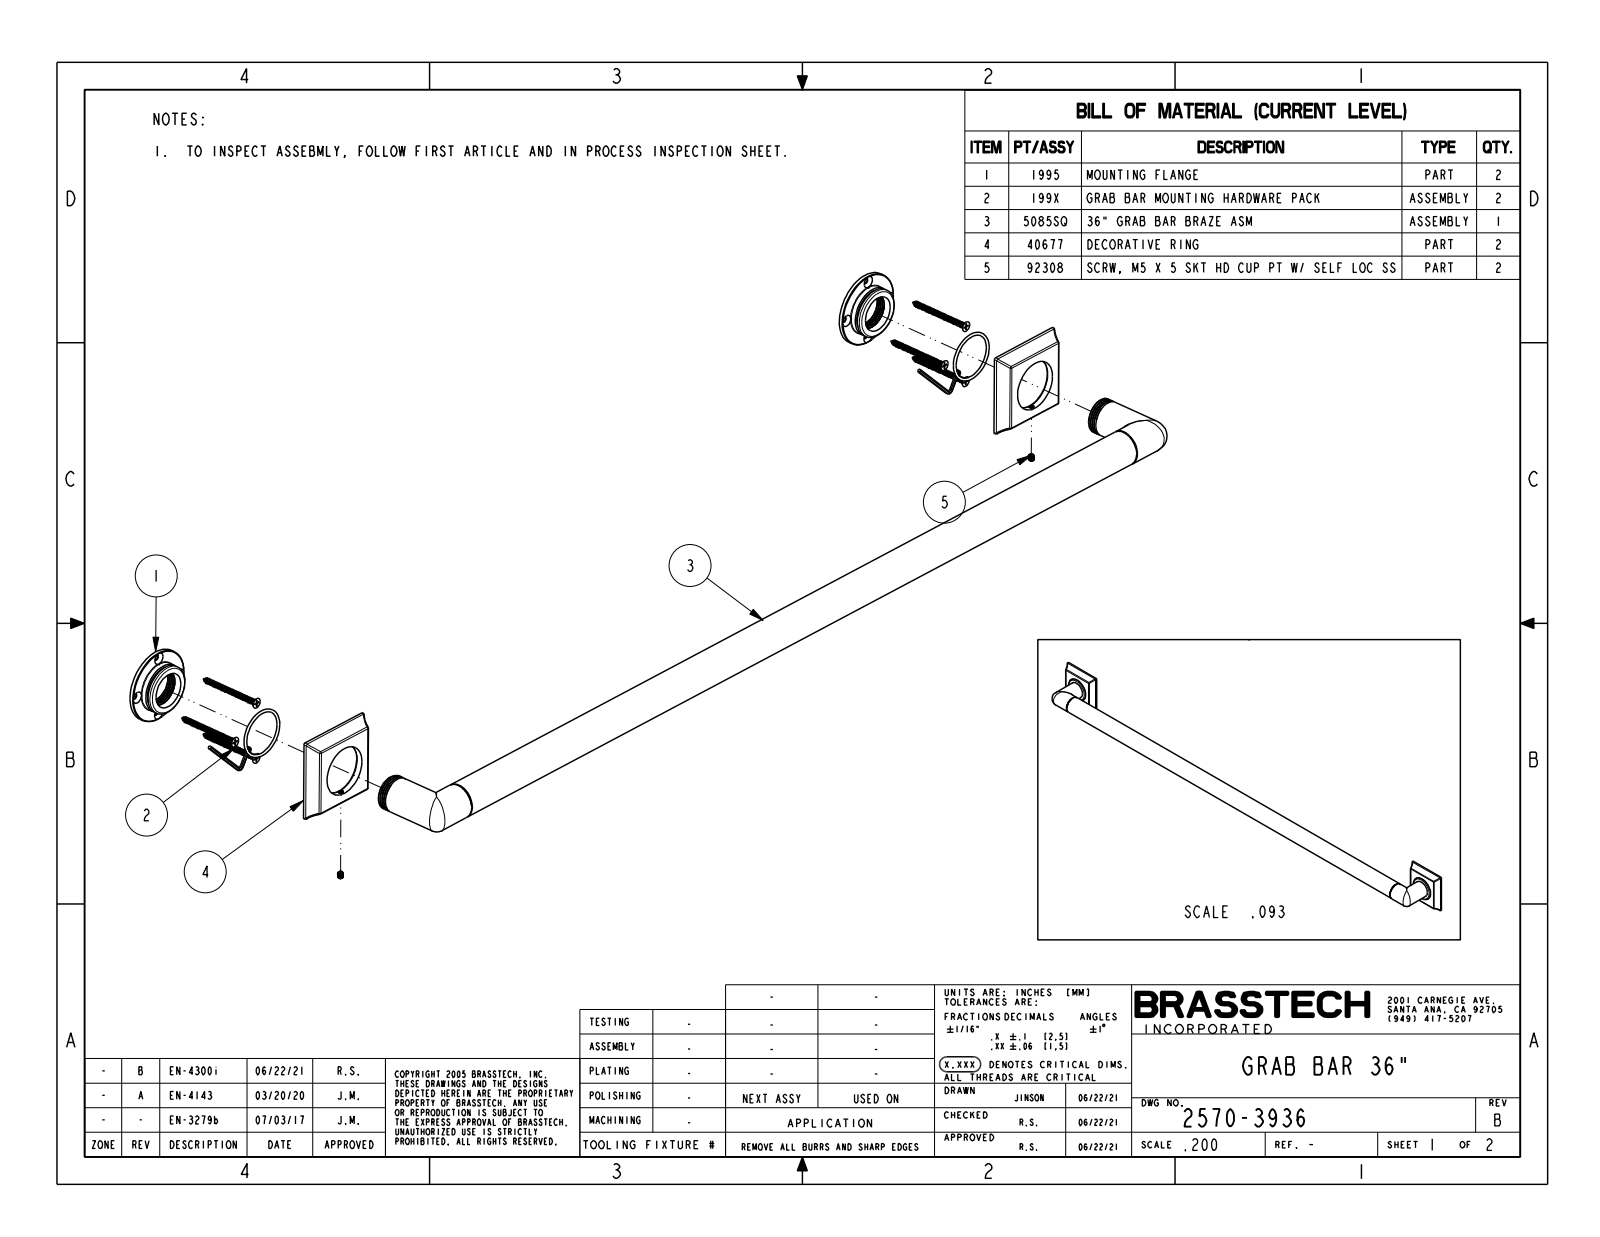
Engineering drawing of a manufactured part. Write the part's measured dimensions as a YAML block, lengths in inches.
part_name: "2570-3936"
step_written_by: "CREO PARAMETRIC BY PTC INC, 2018400 (CONFIG_CONTROL_DESIGN)"
units: inches
bodies: {solids: 1, faces: 88, planar: 6, cylindrical: 38, other: 44}
overall_size: [39, 3, 2.755]
volume: 55.94
surface_area: 193.9
round_bosses_or_shafts:
  - {diameter: 1.25, count: 3}
  - {diameter: 1.75, count: 2}
partial_cylinders:
  - {radius: 0.06, count: 6}
  - {radius: 0.125, count: 6}
  - {radius: 1.35, count: 6}
face_to_face_distances: [0.525, 0.6, 0.075]
